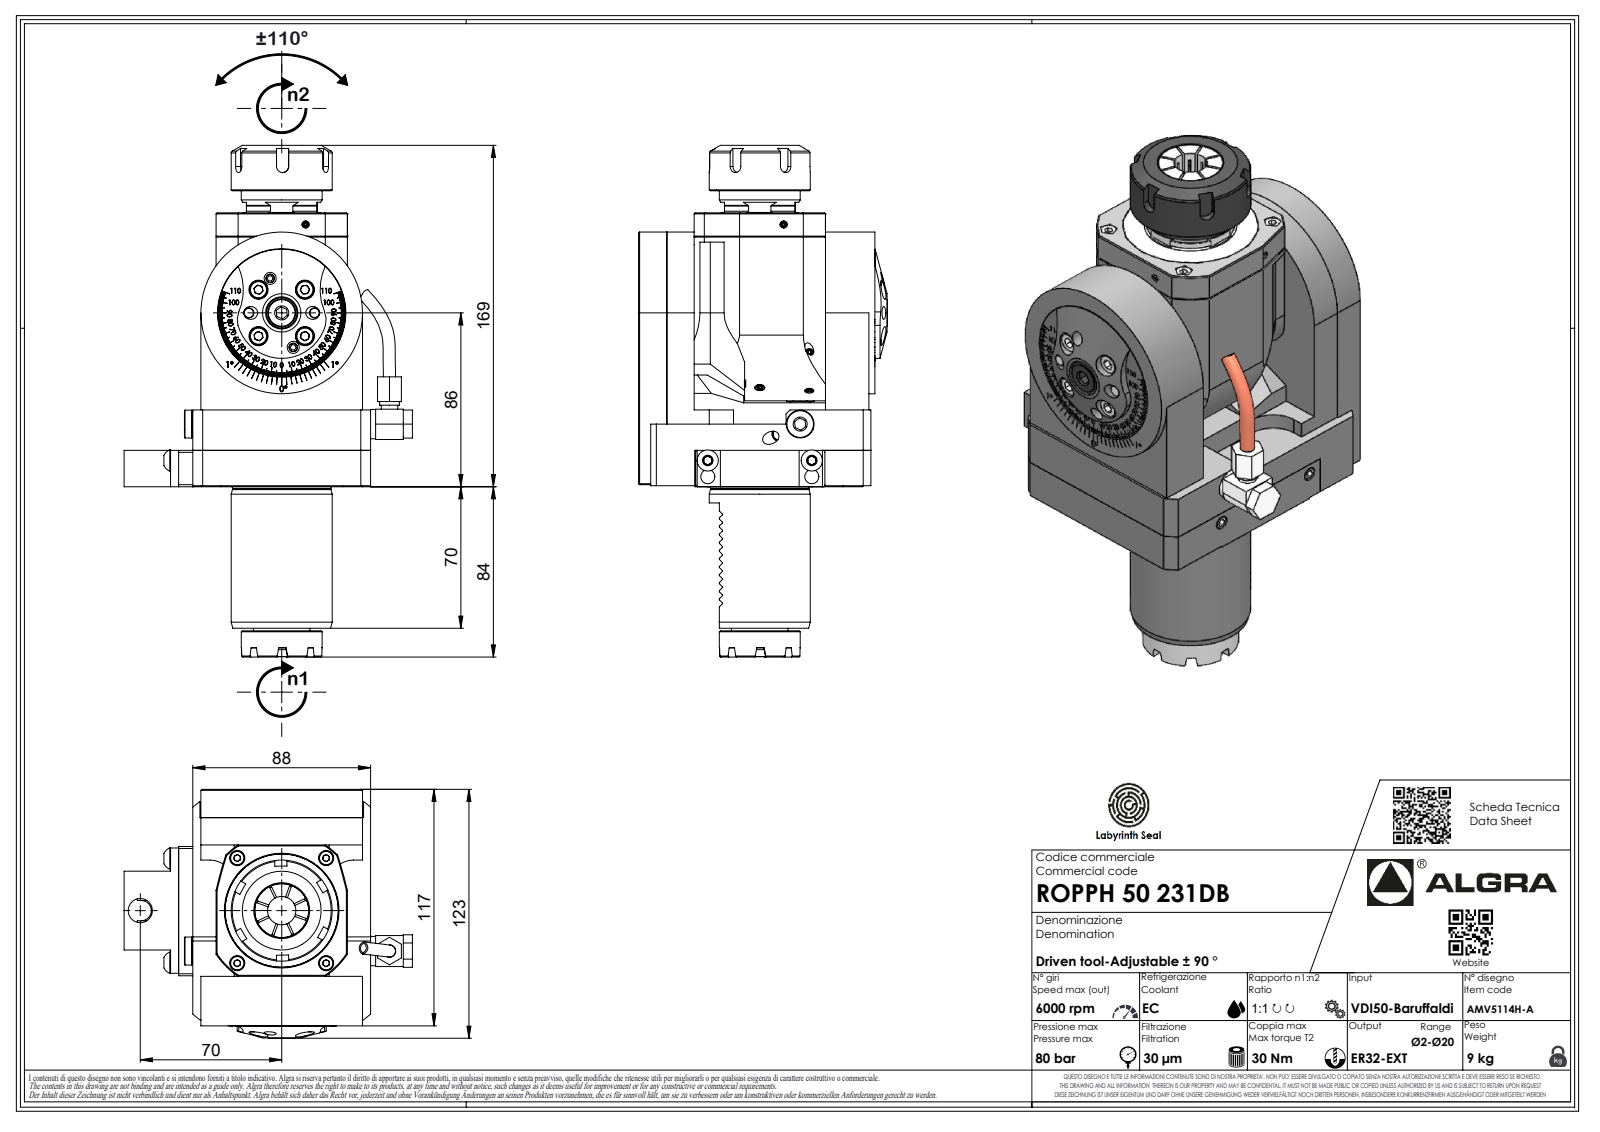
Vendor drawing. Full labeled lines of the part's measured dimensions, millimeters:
Part name (STEP PRODUCT): ROPPH50231DB
STEP written by: SolidWorks 2023 (AUTOMOTIVE_DESIGN)
Units: millimetres
Bodies: 1 solid, 695 faces (426 planar, 129 cylindrical, 140 other)
Overall size (bounding box): 253.16 × 142.7 × 123
Volume: 1 276 000 mm³ · Surface area: 116 831 mm²
Round holes (diameter × count): ⌀2.1 ×1, ⌀44.2 ×1, ⌀48.2 ×1, ⌀52.2 ×1, ⌀56.2 ×1
Round bosses / shafts (diameter × count): ⌀80 ×1, ⌀56 ×1, ⌀52 ×1, ⌀50 ×1, ⌀48.7 ×1, ⌀48 ×1, ⌀44 ×1, ⌀40 ×1
Partial cylindrical surfaces — rounded edges, fillets, slot ends (radius × count): R0.2 ×16, R0.3 ×12, R0.33 ×7, R0.52 ×7, R3.7 ×7, R3 ×5, R1 ×4, R10 ×2
Main face-to-face distances: 4, 65, 84, 0.5, 76.5, 11.5, 22.5, 87.5, 7.5, 72.5
